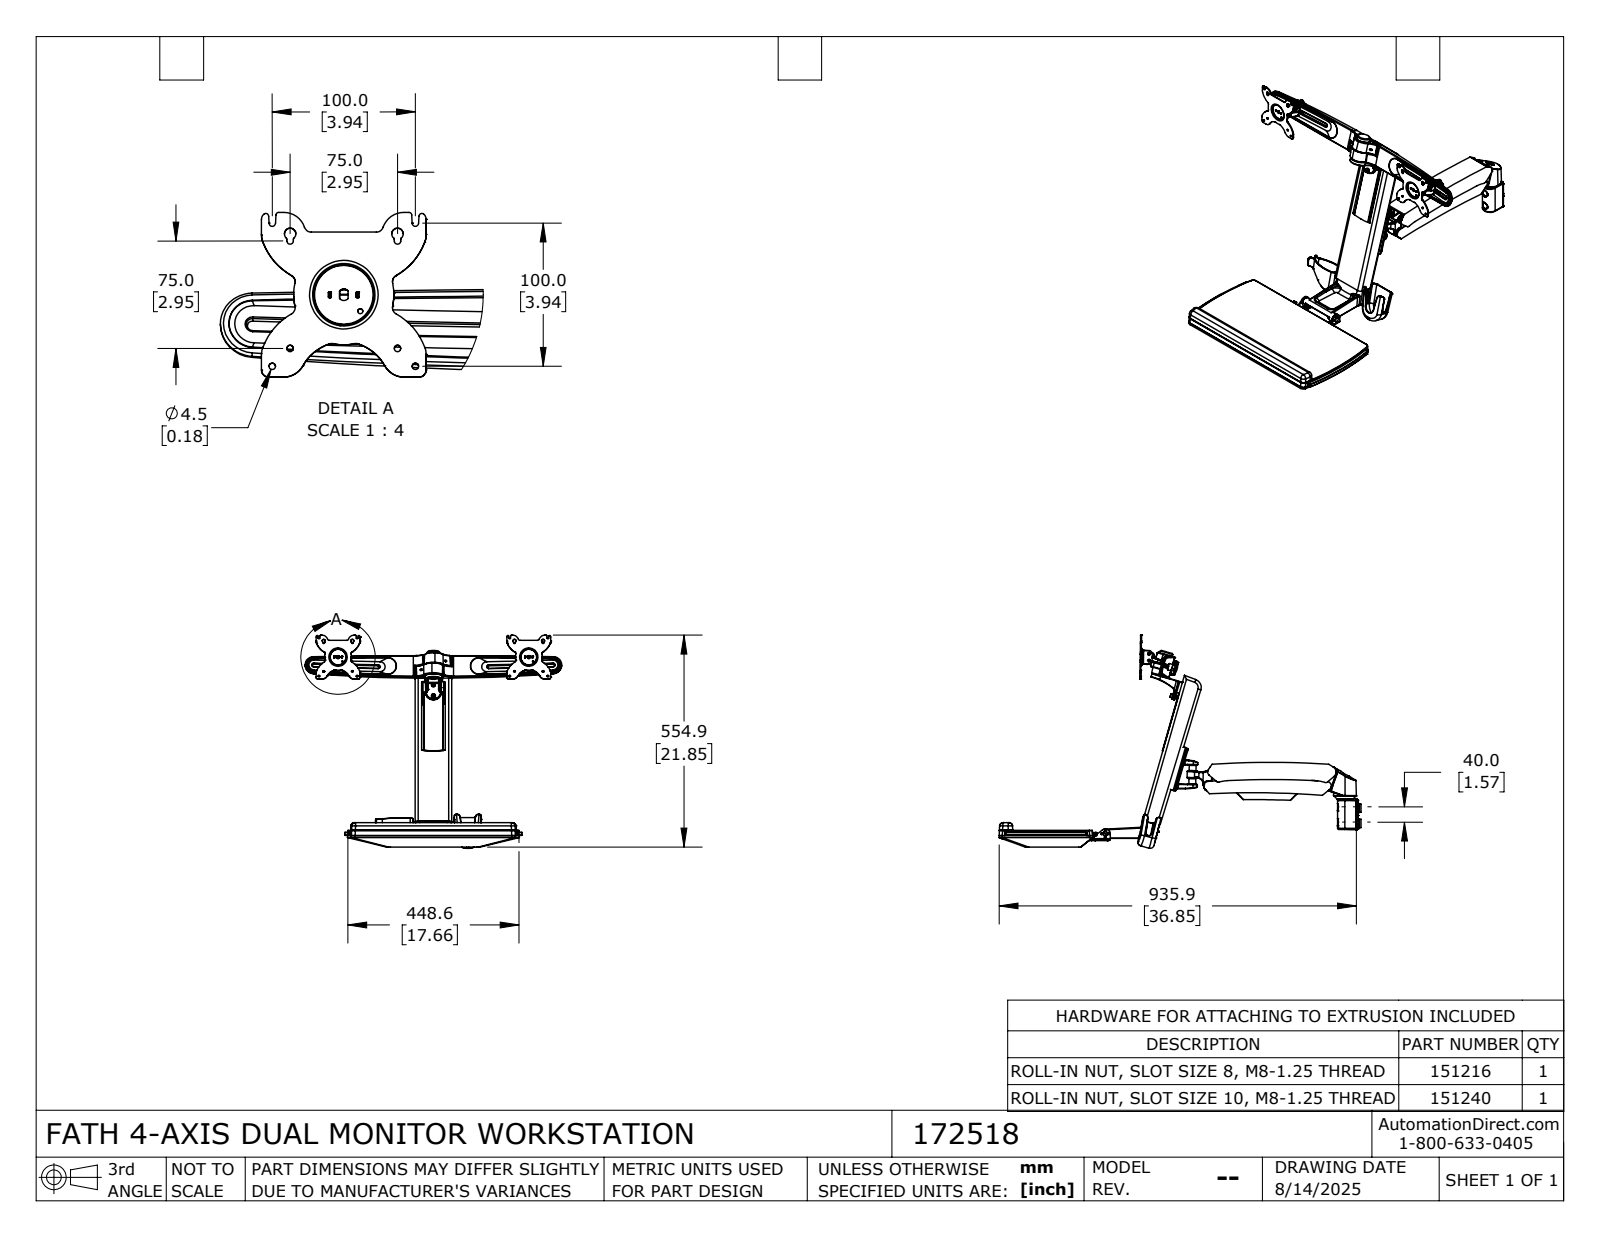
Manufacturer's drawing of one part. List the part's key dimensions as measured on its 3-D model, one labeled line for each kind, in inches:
Part name (STEP PRODUCT): 172518
STEP written by: SolidWorks 2024 (CONFIG_CONTROL_DESIGN)
Units: inches
Bodies: 49 solids, 7037 faces (1244 planar, 2215 cylindrical, 3578 other)
Overall size (bounding box): 37.309 × 26.457 × 21.976
Volume: 347.9 in³ · Surface area: 2 571 in²
Round holes (diameter × count): ⌀0.177 ×18, ⌀0.138 ×15, ⌀0.197 ×11, ⌀0.079 ×9, ⌀0.071 ×8, ⌀0.319 ×6, ⌀0.551 ×6, ⌀0.098 ×5, ⌀0.317 ×5, ⌀0.354 ×5, ⌀0.236 ×4, ⌀0.268 ×3
Round bosses / shafts (diameter × count): ⌀0.315 ×5, ⌀0.709 ×3, ⌀0.256 ×3, ⌀0.217 ×3, ⌀0.866 ×2, ⌀0.512 ×2, ⌀0.394 ×2, ⌀0.237 ×2
Partial cylindrical surfaces — rounded edges, fillets, slot ends (radius × count): R0.02 ×383, R0.012 ×184, R0.039 ×126, R0.118 ×59, R0.024 ×55, R0.079 ×51, R0.197 ×37, R0.098 ×36
Main face-to-face distances: 0.335, 0.315, 0.02, 0.531, 0.465, 0.217, 0.445, 0.13, 0.551, 0.087
Hole centre spacings: 0.696, 3.48, 0.266, 2.953, 3.937, 19.67, 0.531, 0.265
